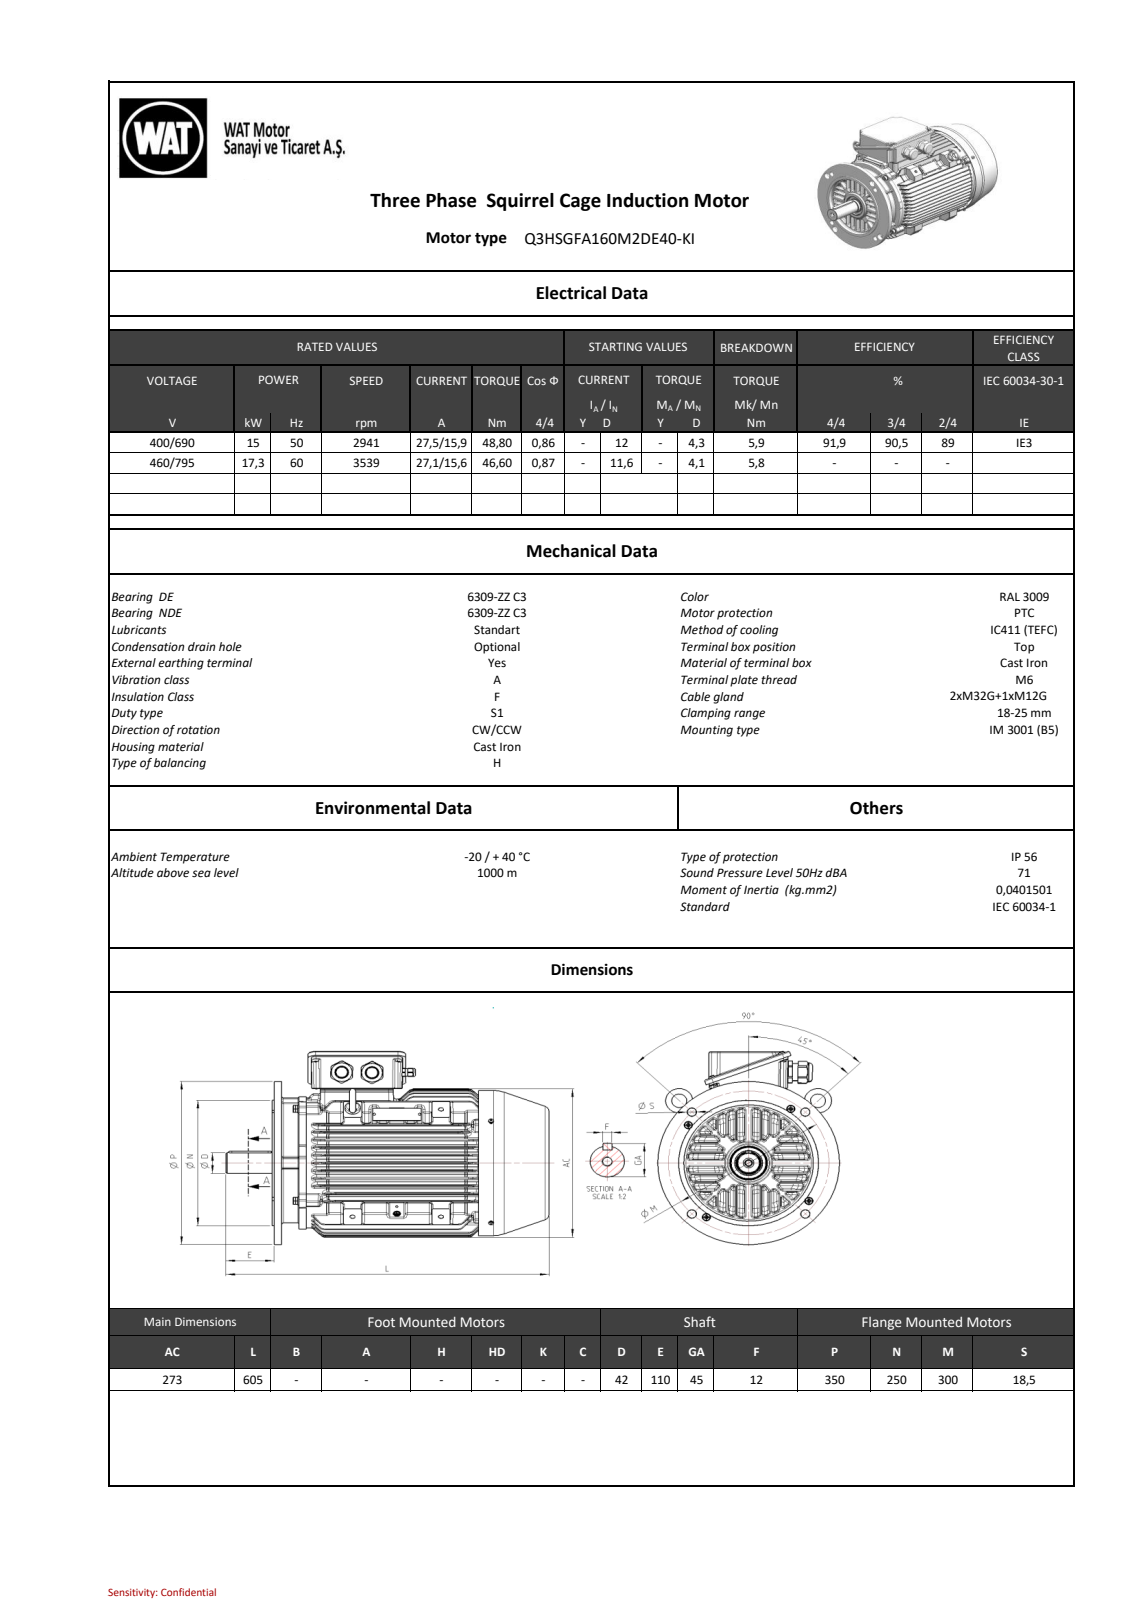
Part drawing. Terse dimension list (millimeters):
name: C9017F38B806sw9t
written by: SIEMENS PLM Software NX 11.0 (AUTOMOTIVE_DESIGN)
unit: mm
bodies: 0 solids, 5573 faces (1019 planar, 1440 cylindrical, 3114 other)
size: 605 × 380.49 × 349
holes: 8× ⌀6.8, 6× ⌀8.5, 4× ⌀15, 2× ⌀2.5, 2× ⌀3.2, 2× ⌀4.2, 2× ⌀10, 2× ⌀19, 2× ⌀21, 1× ⌀13, 1× ⌀68.67, 1× ⌀180
bosses: 4× ⌀10, 4× ⌀8.65, 4× ⌀8, 4× ⌀5, 2× ⌀36, 2× ⌀34.5, 2× ⌀31.25, 2× ⌀25
rounds: 262× R4, 140× R3, 106× R1.5, 83× R2, 60× R1.8, 24× R35, 24× R37, 24× R44
face distances: 6.5, 13.83, 13.76, 27.59, 41.49, 27.73, 13.9, 55.44, 41.68, 27.85
hole spacings: 73.55, 121.5, 171.83, 38.57, 42.2, 139.38, 146, 199.06
